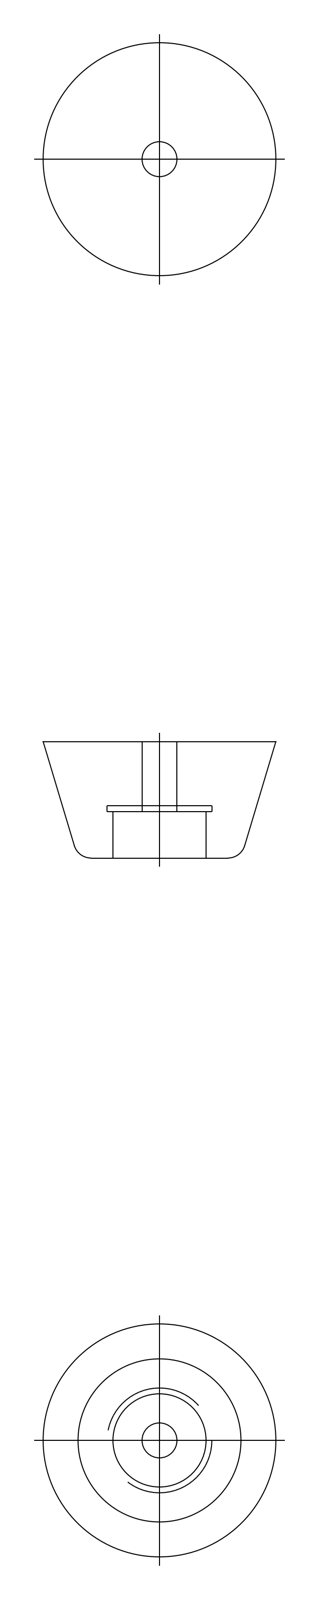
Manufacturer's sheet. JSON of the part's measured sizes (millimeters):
{"part_name": "washer; rubber foot", "step_written_by": "spGate 15.6.1 (AUTOMOTIVE_DESIGN)", "units": "millimeters", "bodies": {"solids": 2, "faces": 20, "planar": 6, "cylindrical": 10, "other": 4}, "overall_size": [20, 20, 10], "volume_mm3": 2044, "surface_area_mm2": 1323, "round_holes": [[3, 1], [8, 1], [9, 1]], "face_to_face_distances": [5.5, 0.5, 6, 4, 4.5, 10]}
